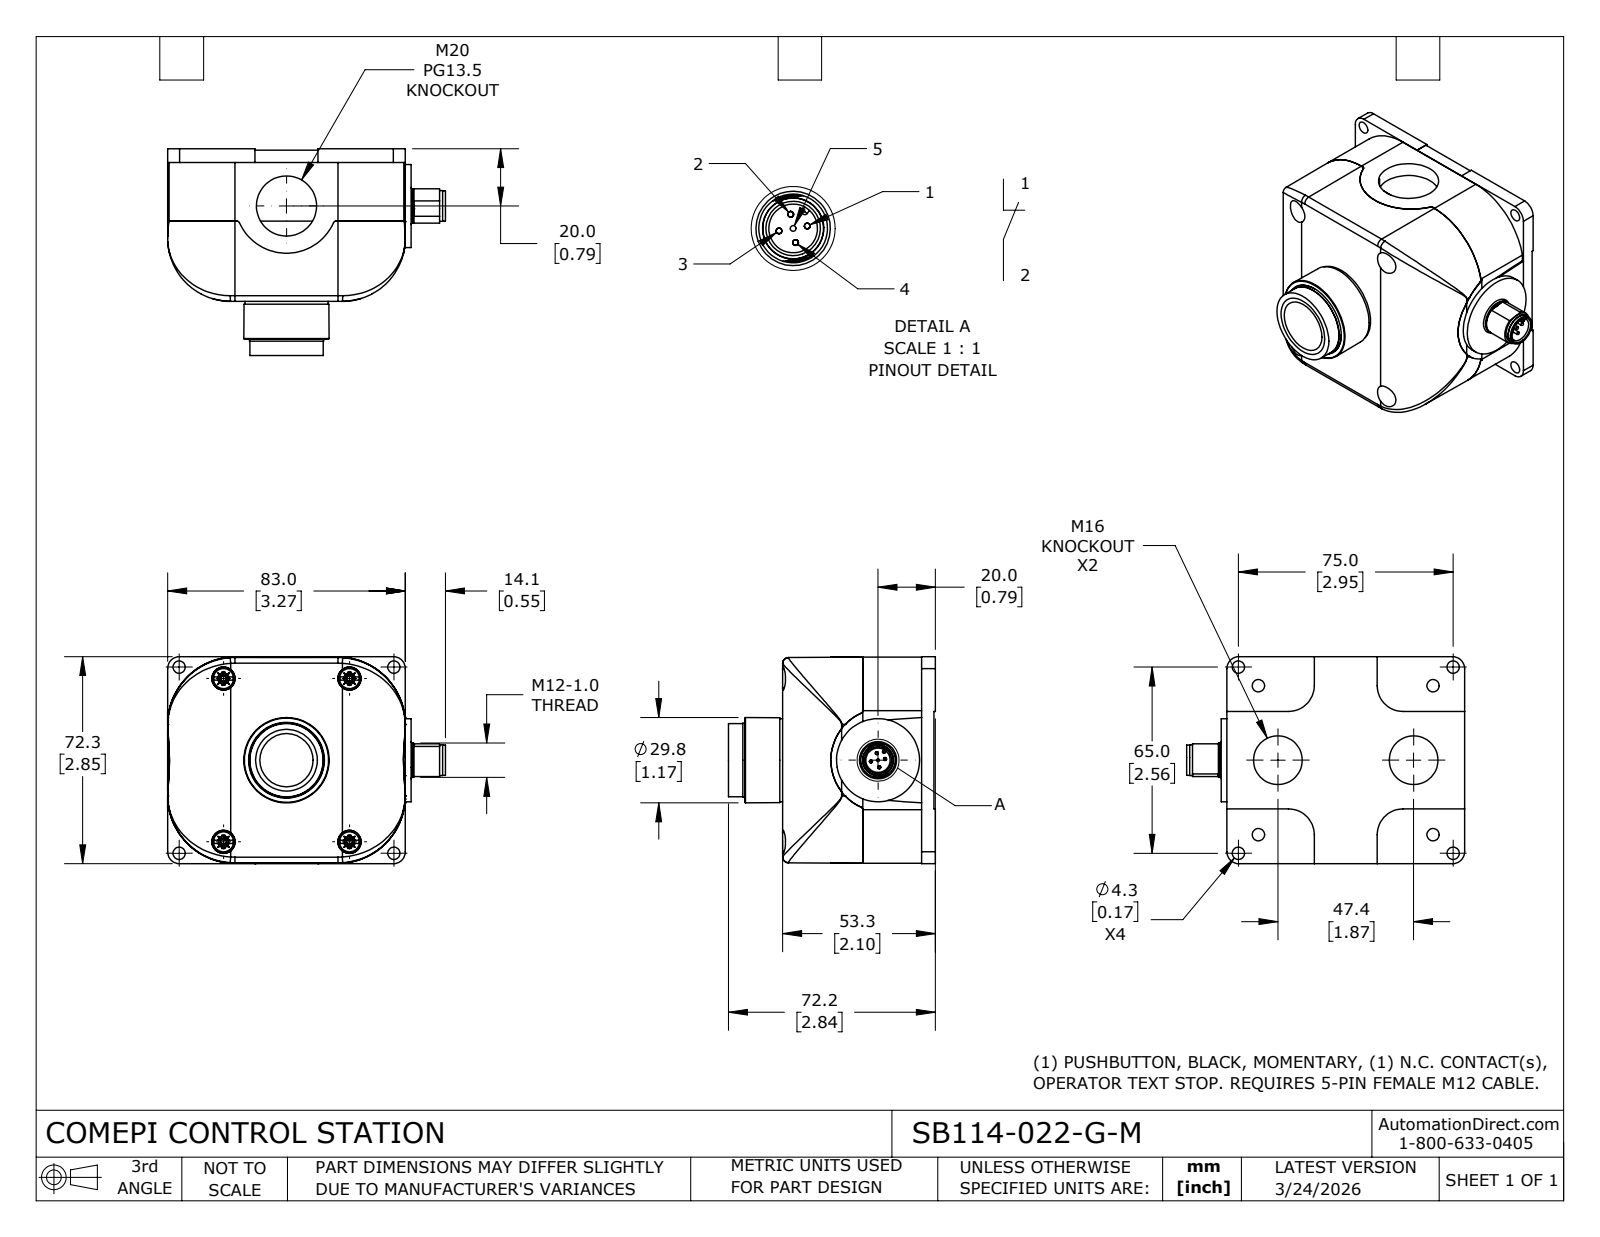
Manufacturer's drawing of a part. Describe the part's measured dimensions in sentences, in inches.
The part is named "SB114-022-G-M". Its 3-D file was written by "SolidWorks 2024 (CONFIG_CONTROL_DESIGN)". It is 10 solids with 789 faces: 371 planar, 275 cylindrical and 143 other. Overall it measures 3.821 by 2.846 by 2.843 inches. Its volume is 13.41 cubic inches and its surface area 96.08 square inches. Round holes: 8 of diameter 0.169, 4 of diameter 0.04, 4 of diameter 0.067, 4 of diameter 0.087, 4 of diameter 0.323, 2 of diameter 0.669, 2 of diameter 0.827, 1 of diameter 0.335, 1 of diameter 0.531, 1 of diameter 0.713, 1 of diameter 0.854. Round bosses or shafts: 5 of diameter 0.039, 4 of diameter 0.276, 4 of diameter 0.085, 4 of diameter 0.065, 2 of diameter 1.142, 2 of diameter 0.024, 1 of diameter 1.039, 1 of diameter 1.02. Partial cylindrical surfaces (rounded edges, fillets, slot ends): 5 of radius 0.02, 4 of radius 0.035, 4 of radius 0.079, 4 of radius 0.354, 4 of radius 0.38, 4 of radius 0.925, 2 of radius 0.008, 2 of radius 0.01. The main face-to-face distances are 0.976, 0.098, 0.878, 2.079, 1.98, 1.102, 0.118, 2.098, 0.02, 0.996. The hole center spacings are 0.376, 1.058, 1.39, 1.578, 1.954, 2.32, 2.367, 2.689.
